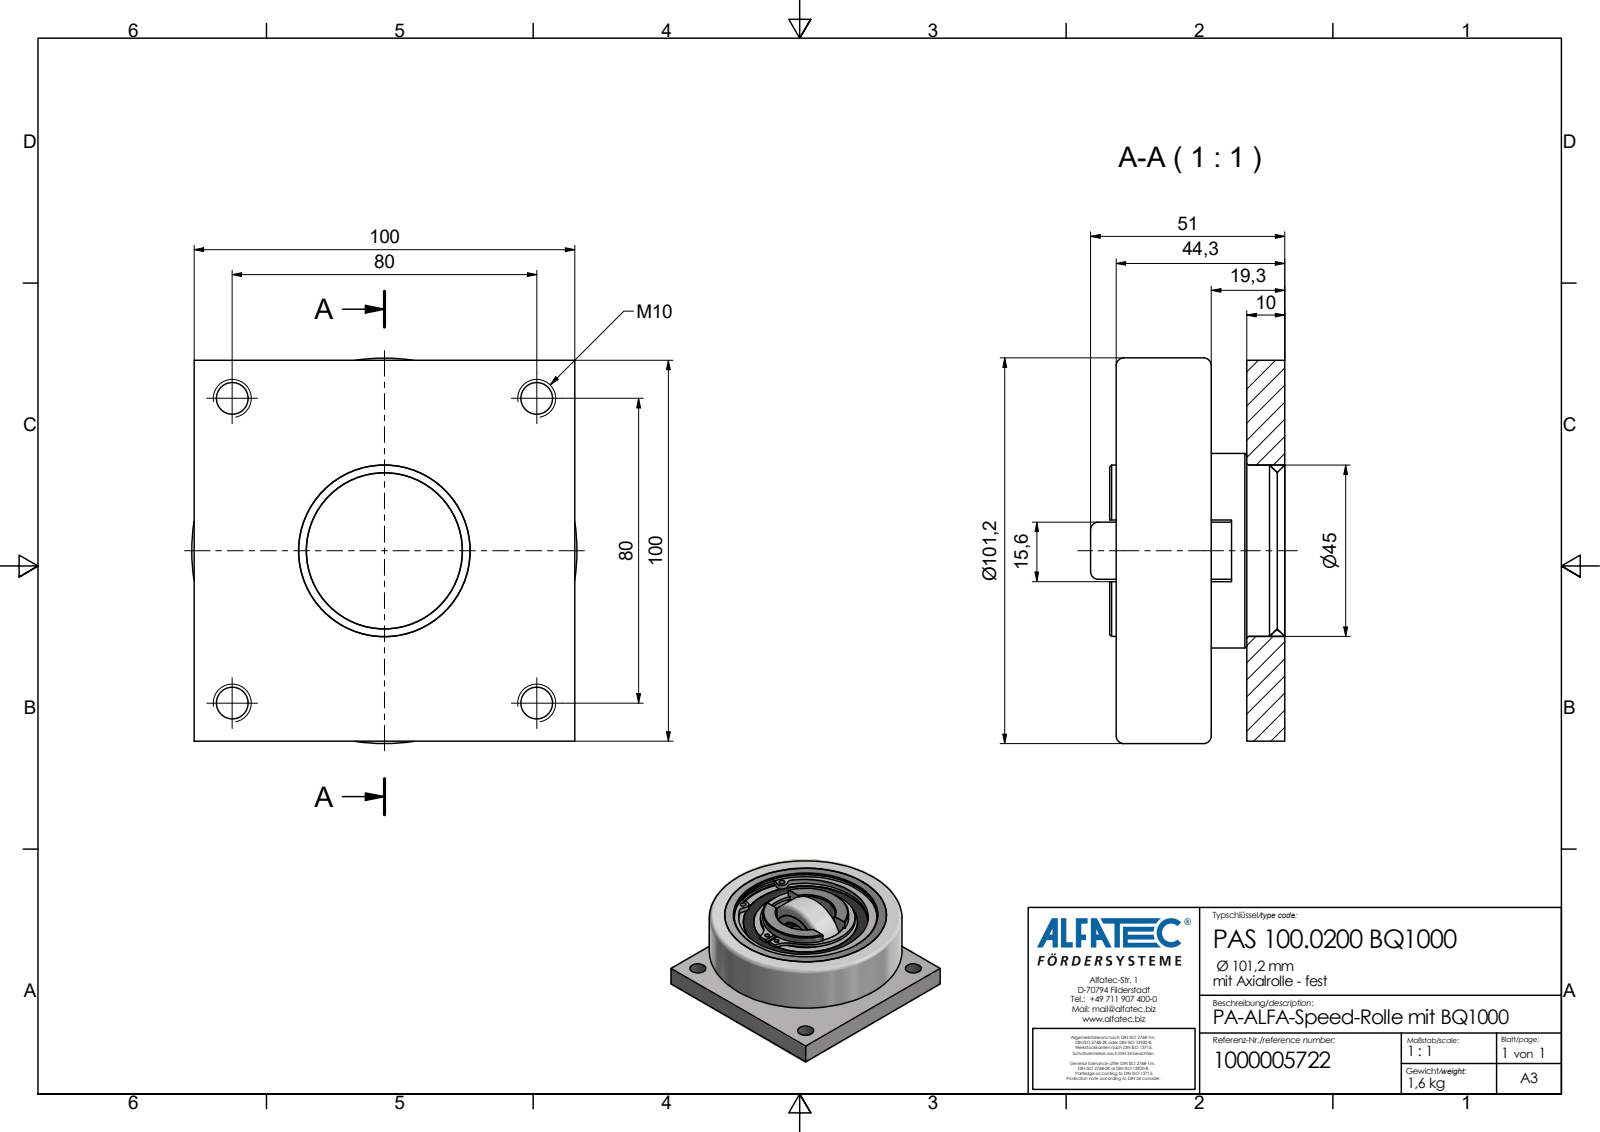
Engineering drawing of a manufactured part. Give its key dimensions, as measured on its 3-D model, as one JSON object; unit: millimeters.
{"part_name": "PAS 100.0200 BQ1000_Kontur", "step_written_by": "Autodesk Inventor 2020 (AP242_MANAGED_MODEL_BASED_3D_ENGINEERING_MIM_LF)", "units": "millimeters", "bodies": {"solids": 1, "faces": 54, "planar": 27, "cylindrical": 15, "other": 12}, "overall_size": [101.2, 101.2, 51], "volume_mm3": 305360, "surface_area_mm2": 48988, "round_holes": [[8.38, 4], [31, 1]], "round_bosses_or_shafts": [[101.2, 1], [51, 1]], "partial_cylinders_radius": [[13, 1], [13.6, 1], [20, 1], [22.5, 1]], "face_to_face_distances": [10, 44.3, 34.3, 19.3, 9.3, 25, 100, 2, 8, 17.3], "hole_center_spacings": [56.57, 80, 113.14]}
